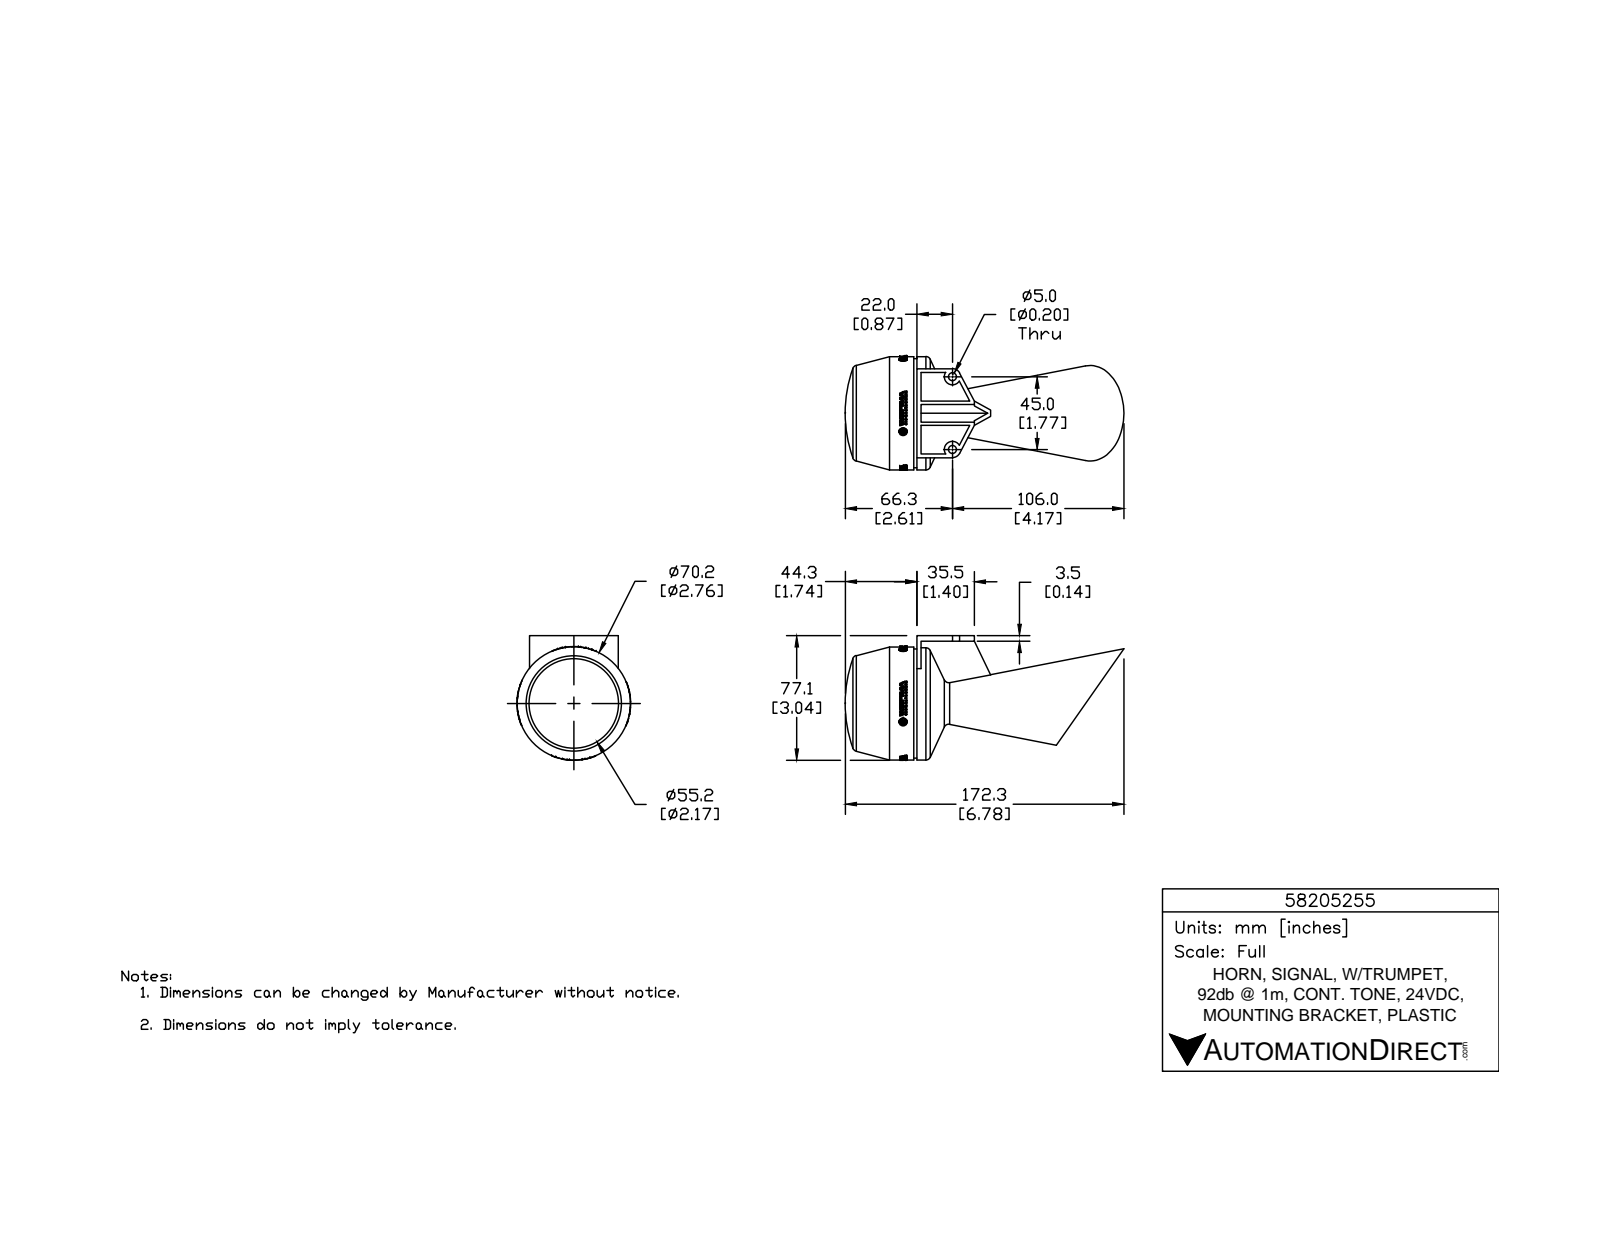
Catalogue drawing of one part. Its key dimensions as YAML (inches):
part_name: "58205255"
step_written_by: "SolidWorks 2017 (AUTOMOTIVE_DESIGN)"
units: inches
bodies: {solids: 1, faces: 1036, planar: 590, cylindrical: 119, other: 327}
overall_size: [6.783, 3.035, 2.764]
volume: 20.08
surface_area: 60.58
round_holes:
  - {diameter: 0.197, count: 2}
round_bosses_or_shafts:
  - {diameter: 2.756, count: 1}
  - {diameter: 2.657, count: 1}
partial_cylinders:
  - {radius: 0.197, count: 2}
  - {radius: 1.382, count: 1}
face_to_face_distances: [0.098, 0.112, 0.112, 0.039, 0.138, 0.177, 0.079, 2.165, 0.787, 1.378]
hole_center_spacings: [1.772]
